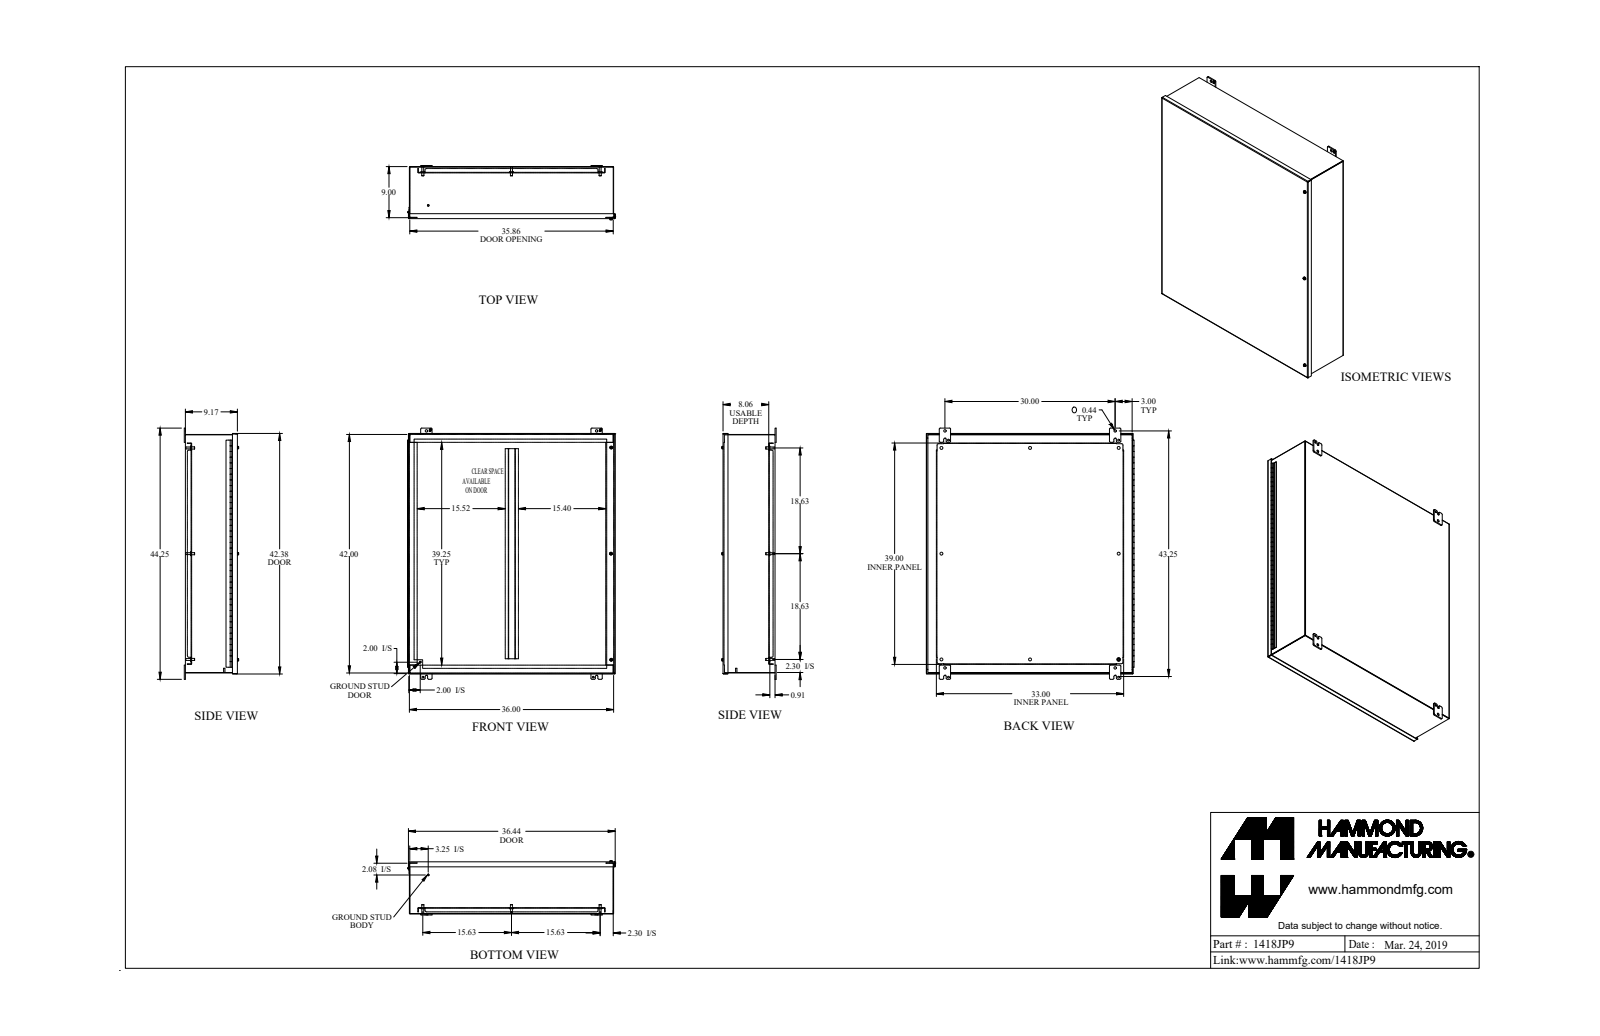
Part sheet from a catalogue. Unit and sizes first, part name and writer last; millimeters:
Units: millimetres
Overall size (bounding box): 1124 × 929.7 × 243.1
Round holes (diameter × count): ⌀12.7 ×8, ⌀8 ×7, ⌀7.8 ×4, ⌀11.1 ×4, ⌀11.3 ×4, ⌀6.6 ×3, ⌀6.8 ×3, ⌀7.1 ×3, ⌀7.4 ×3, ⌀10.1 ×3, ⌀4.7 ×1, ⌀88.9 ×1
Round bosses / shafts (diameter × count): ⌀16.5 ×8, ⌀9.5 ×8, ⌀8.4 ×8, ⌀25.4 ×4, ⌀13 ×3, ⌀12.7 ×3, ⌀9.9 ×3, ⌀6.2 ×3
Partial cylindrical surfaces — rounded edges, fillets, slot ends (radius × count): R4.8 ×34, R6.4 ×28, R2.9 ×16, R0.9 ×10, R2.7 ×10, R5.5 ×8, R3.2 ×7, R3.4 ×6
Main face-to-face distances: 1.8, 231.1, 229.3, 233, 2.4, 28, 26.2, 203.1, 204.9, 25.6
Hole centre spacings: 946.2, 1235, 44.1, 77.9, 396.9, 473.1, 474.6, 474.7
Volume: 9 046 000 mm³ · Surface area: 8 963 000 mm²
Bodies: 50 solids, 1367 faces (790 planar, 499 cylindrical, 78 other)
Part name (STEP PRODUCT): 1418JP9_Default
STEP written by: SolidWorks 2018 (CONFIG_CONTROL_DESIGN)
